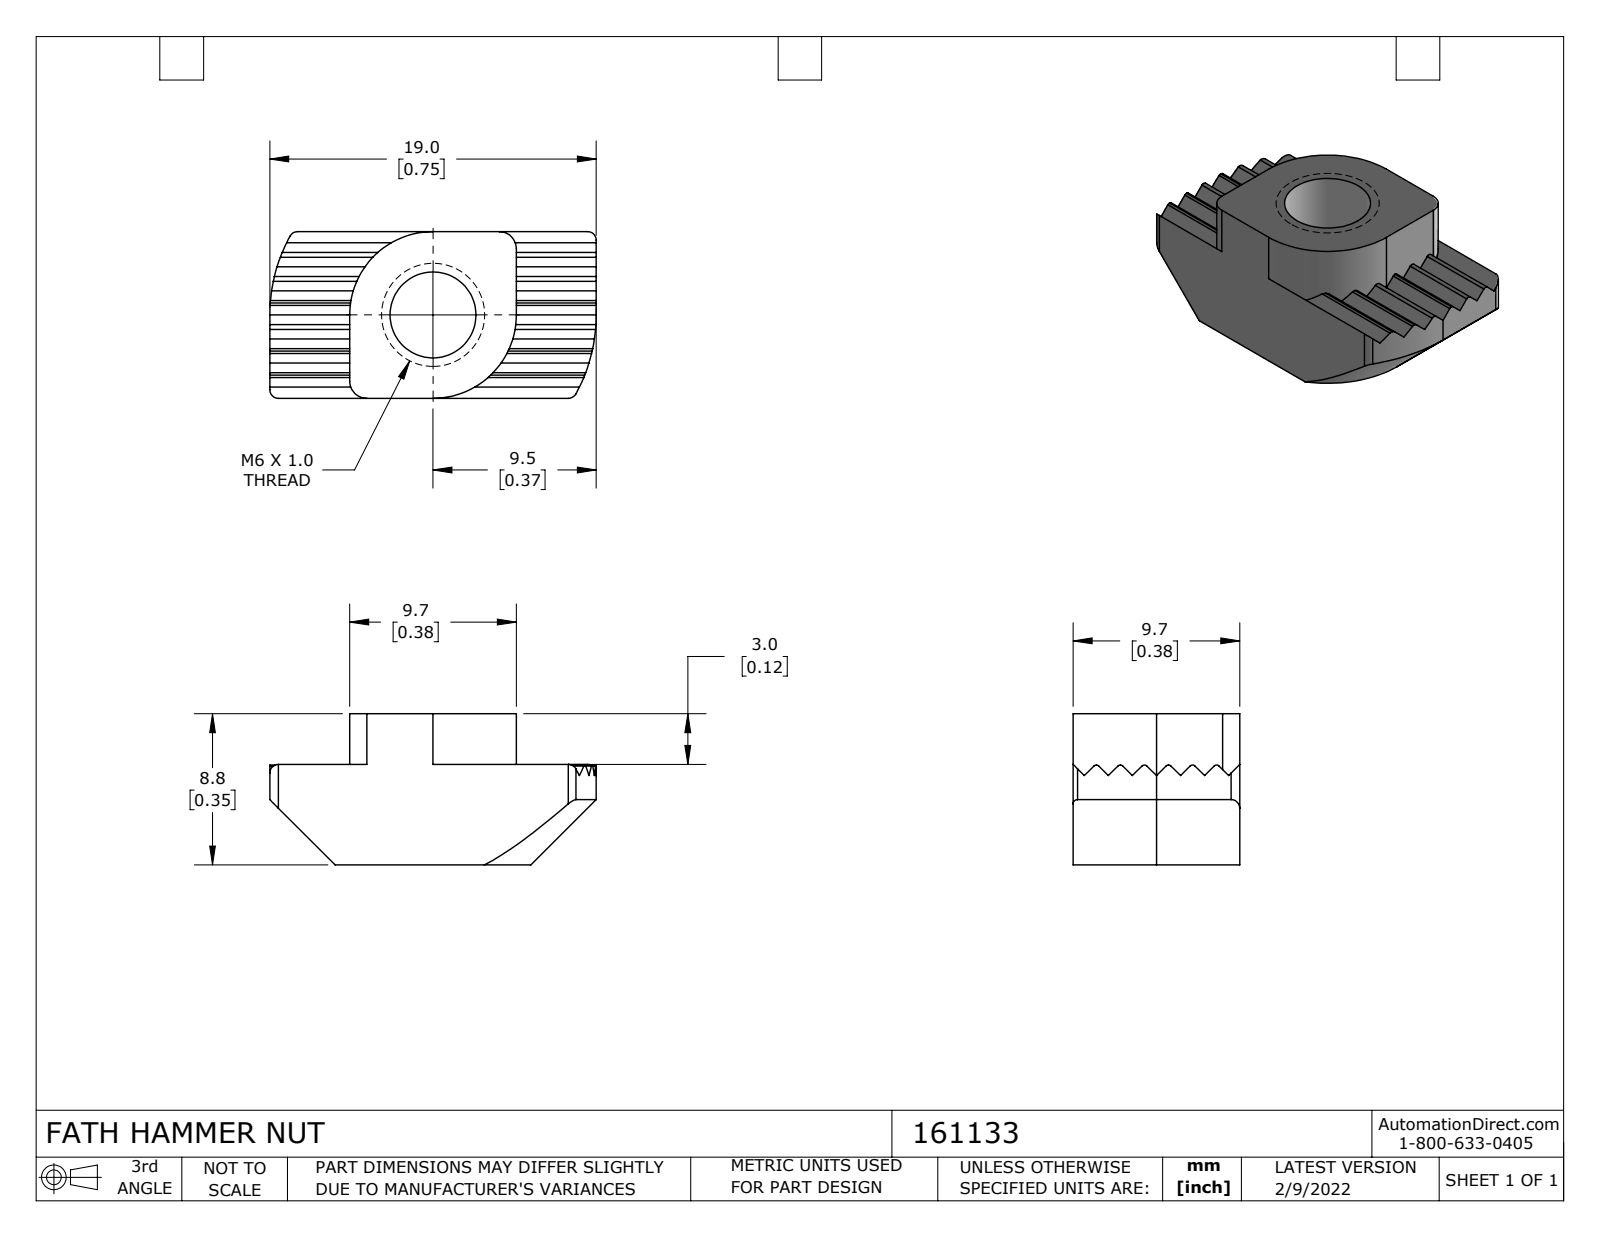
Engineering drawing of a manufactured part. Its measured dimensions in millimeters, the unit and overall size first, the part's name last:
Units: millimetres
Overall size (bounding box): 19 × 9.7 × 8.8
Round holes (diameter × count): ⌀5 ×1
Partial cylindrical surfaces — rounded edges, fillets, slot ends (radius × count): R0.2 ×6, R0.5 ×4, R1 ×2, R4.85 ×1, R9.5 ×1
Main face-to-face distances: 9.7, 0.99, 1.98, 8.8, 2.97, 3.96, 4.95, 5.94, 4.65, 14.35
Volume: 952 mm³ · Surface area: 840 mm²
Bodies: 1 solid, 70 faces (38 planar, 30 cylindrical, 2 other)
Part name (STEP PRODUCT): 161133
STEP written by: SolidWorks 2021 (CONFIG_CONTROL_DESIGN)
